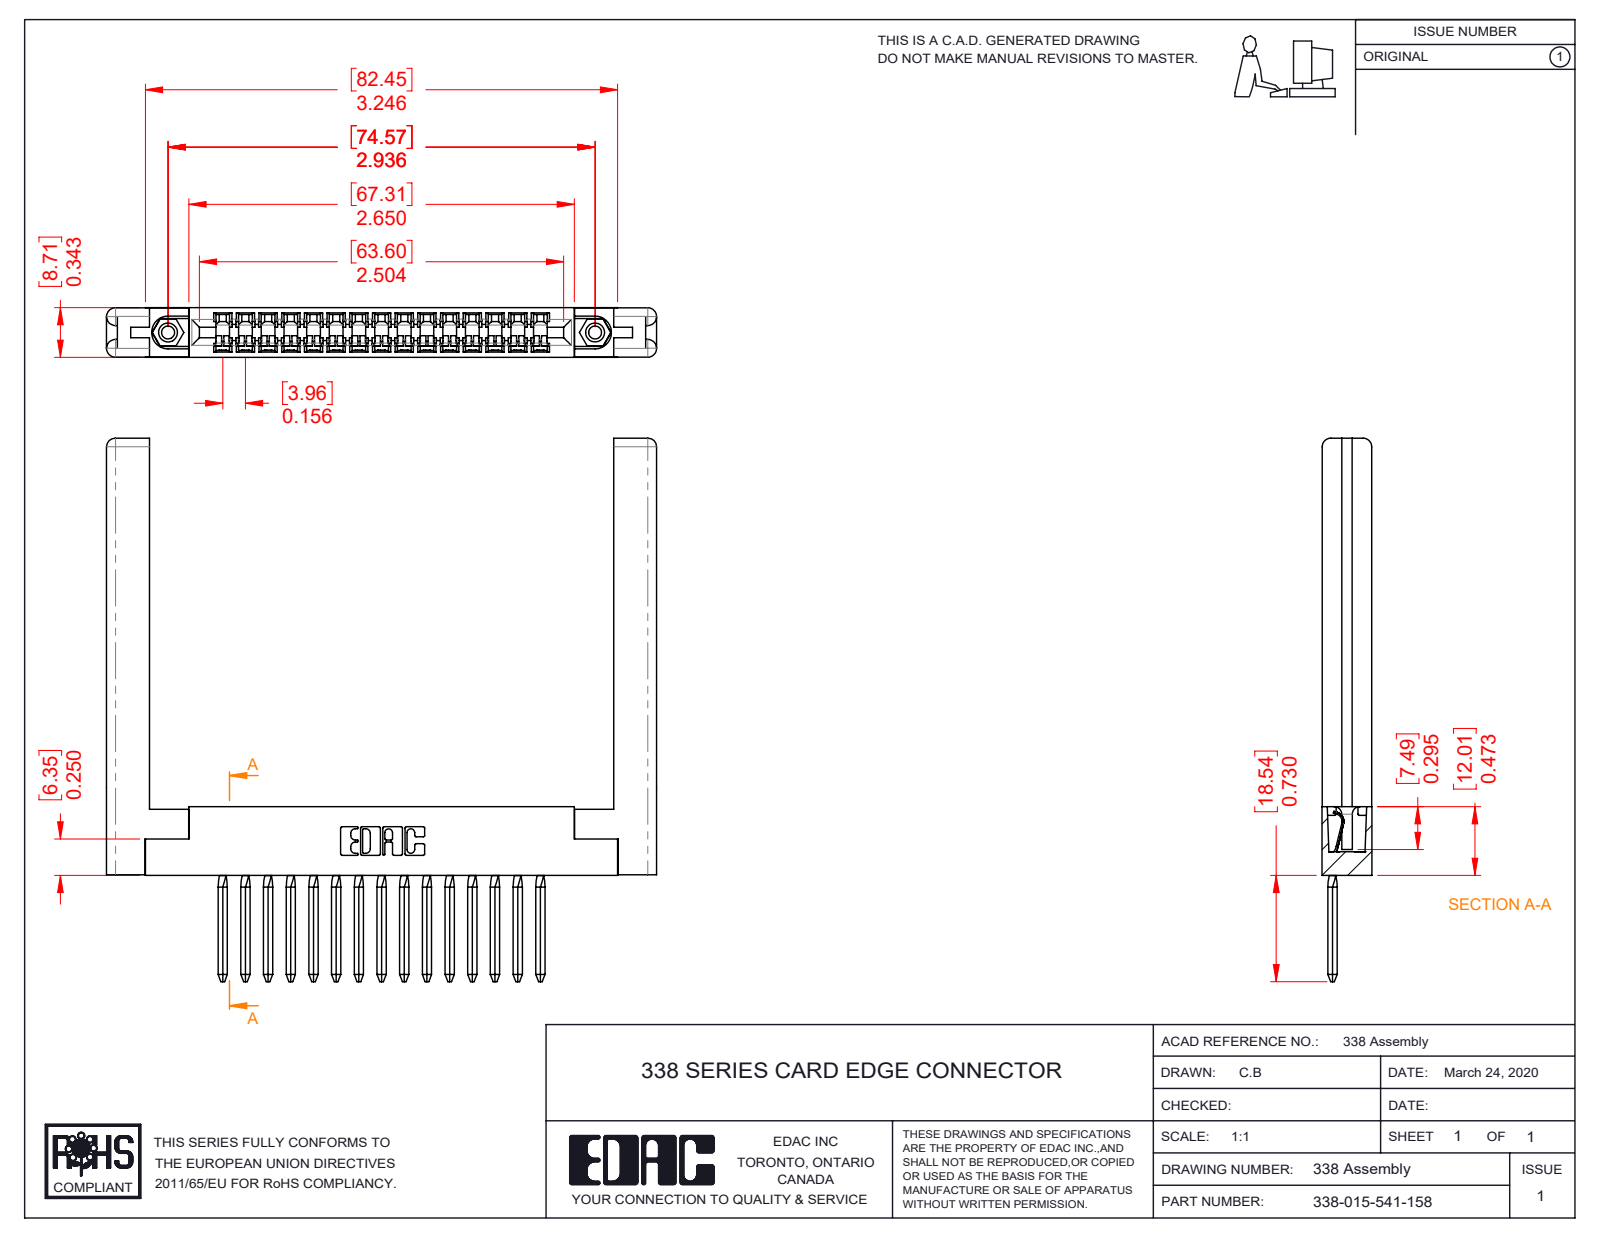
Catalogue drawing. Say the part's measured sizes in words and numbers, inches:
The part is named "338-290-001_541; 345-250-001_345-250-001-102; 338-210-001_338-210-015-004; 307-220-058 (+1 more)". Its 3-D file was written by "SolidWorks 2016 (CONFIG_CONTROL_DESIGN)". It is 20 solids with 1631 faces: 1109 planar, 438 cylindrical and 84 other. Overall it measures 3.782 by 3.735 by 0.343 inches. Its volume is 0.874 cubic inches and its surface area 24.2 square inches. Round holes: 2 of diameter 0.089, 2 of diameter 0.125, 2 of diameter 0.156. Round bosses or shafts: 2 of diameter 0.155. Partial cylindrical surfaces (rounded edges, fillets, slot ends): 62 of radius 0.025, 22 of radius 0.01, 15 of radius 0.008, 12 of radius 0.055, 12 of radius 0.067, 12 of radius 0.1, 8 of radius 0.061, 6 of radius 0.007. The main face-to-face distances are 0.341, 0.34, 0.136, 0.343, 0.207, 0.134, 0.206, 3.192, 0.22, 0.071. The hole center spacings are 2.936.
